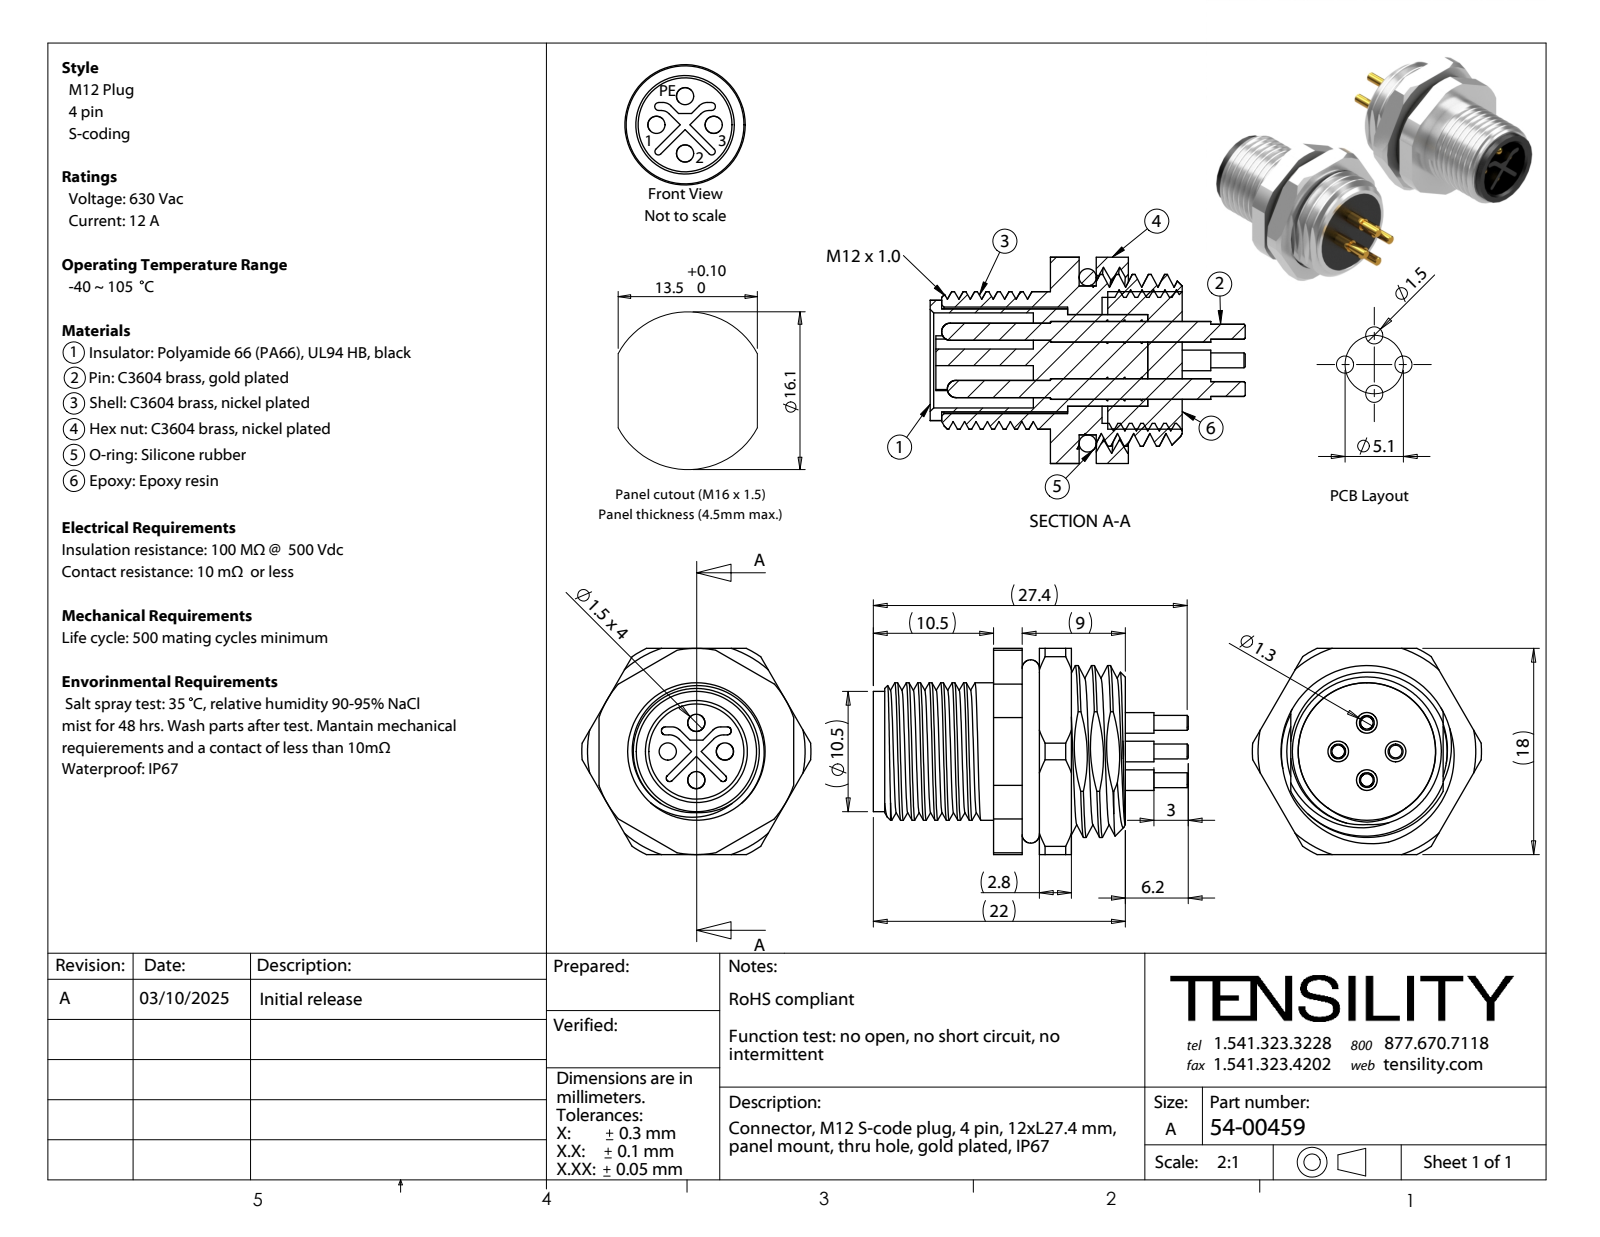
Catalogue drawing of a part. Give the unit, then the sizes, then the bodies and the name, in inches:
Units: inches
Overall size (bounding box): 1.083 × 0.787 × 0.709
Round holes (diameter × count): ⌀0.059 ×4, ⌀0.315 ×1, ⌀0.327 ×1, ⌀0.366 ×1, ⌀0.433 ×1, ⌀0.551 ×1
Round bosses / shafts (diameter × count): ⌀0.071 ×4, ⌀0.051 ×4, ⌀0.512 ×1, ⌀0.472 ×1, ⌀0.413 ×1, ⌀0.354 ×1
Partial cylindrical surfaces — rounded edges, fillets, slot ends (radius × count): R0.012 ×2, R0.014 ×2, R0.039 ×2, R0.05 ×2, R0.295 ×1, R0.354 ×1, R0.394 ×1
Main face-to-face distances: 0.098, 0.157, 0.059, 0.118, 0.453, 0.354, 0.177, 0.236, 0.039, 0.709
Hole centre spacings: 0.098, 0.139, 0.197
Volume: 0.186 in³ · Surface area: 9.162 in²
Bodies: 9 solids, 340 faces (87 planar, 159 cylindrical, 94 other)
Part name (STEP PRODUCT): 54-00459; 54-00459-02; 54-00459-03; 54-00459-04 (+3 more)
STEP written by: SolidWorks 2021 (CONFIG_CONTROL_DESIGN)
